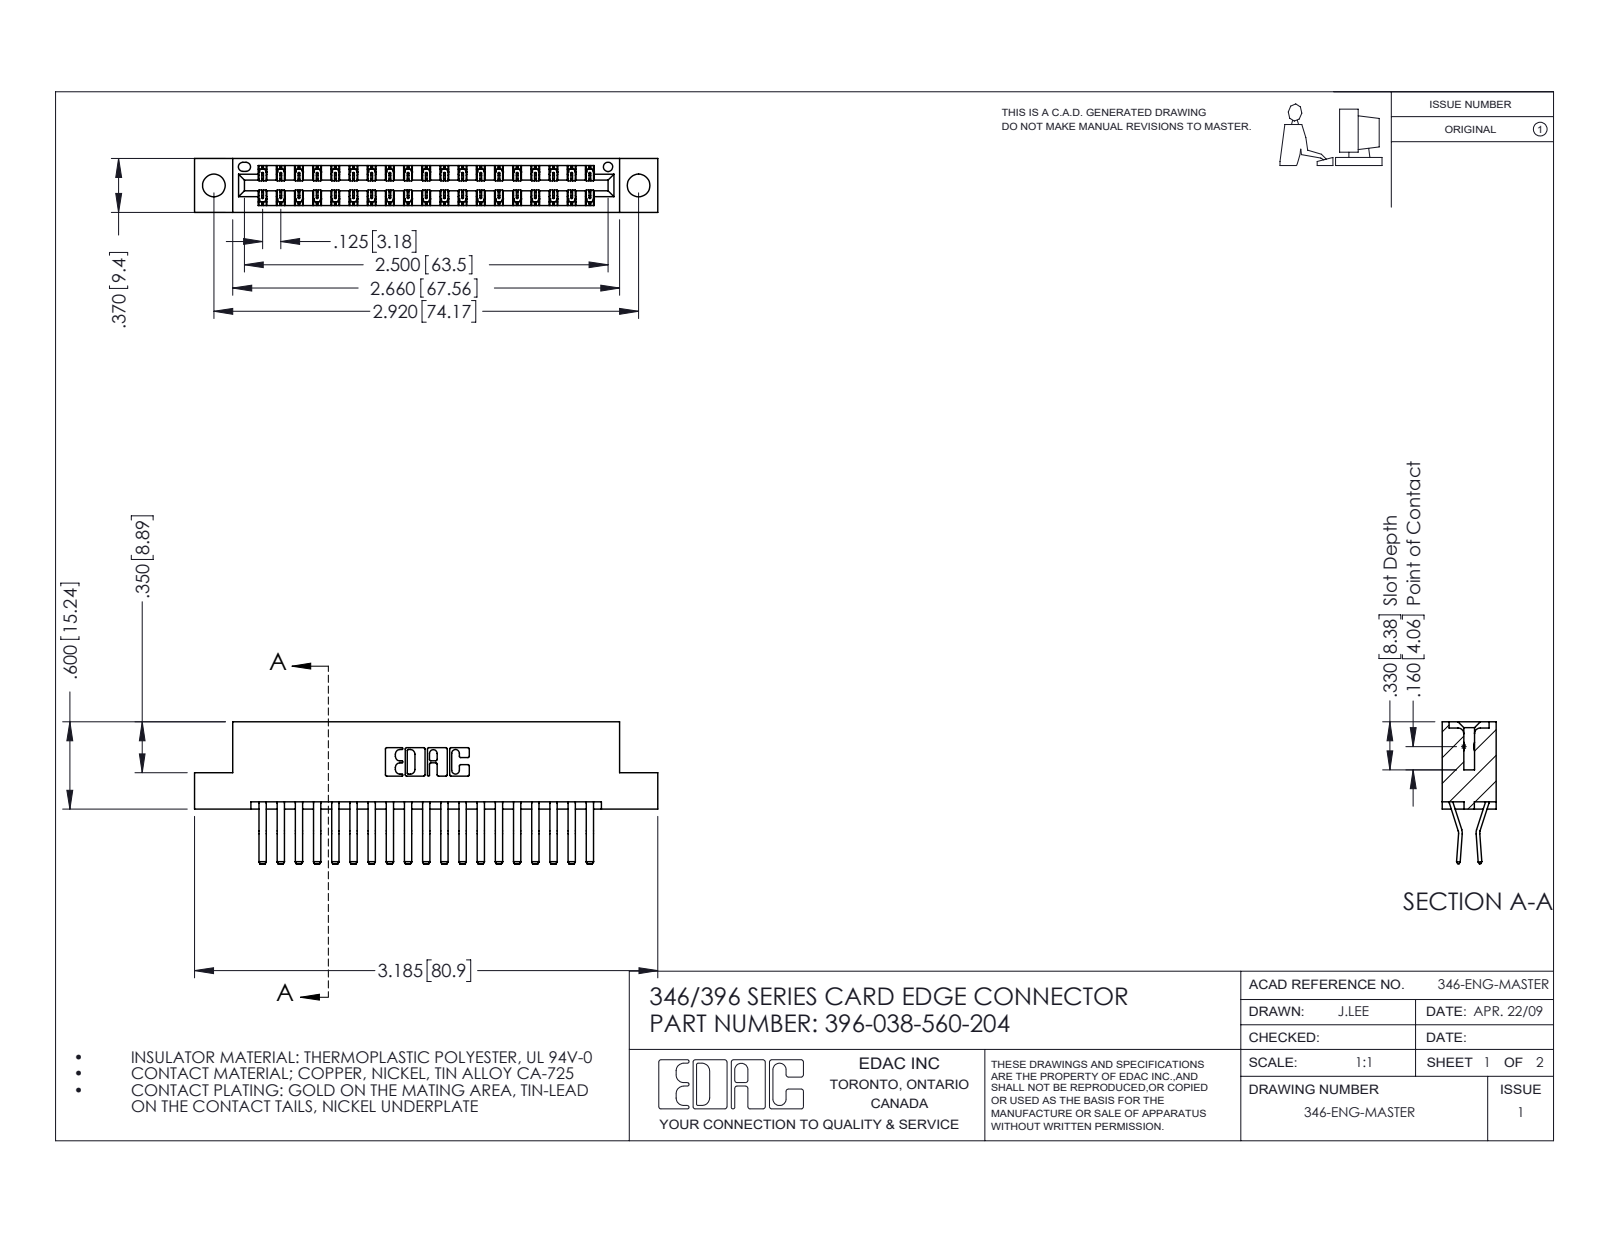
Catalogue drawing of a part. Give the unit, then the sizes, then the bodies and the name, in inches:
Units: inches
Overall size (bounding box): 3.185 × 0.975 × 0.37
Round holes (diameter × count): ⌀0.156 ×2, ⌀0.064 ×1
Partial cylindrical surfaces — rounded edges, fillets, slot ends (radius × count): R0.006 ×57, R0.01 ×22, R0.007 ×6, R0.031 ×6, R0.026 ×3, R0.01 ×2, R0.014 ×2, R0.022 ×2
Main face-to-face distances: 0.048, 0.322, 0.25, 0.37, 0.025, 0.072, 0.298, 0.275, 0.148, 0.222
Hole centre spacings: 0.246, 2.713, 2.92
Volume: 0.48 in³ · Surface area: 16.95 in²
Bodies: 39 solids, 2174 faces (1406 planar, 768 cylindrical, 0 other)
Part name (STEP PRODUCT): 396-038-560-204; 346 Part_Flush Mounting Lugs - 0.156 Dia-TH; 345-292-001_560 Tail
STEP written by: SolidWorks 2016 (CONFIG_CONTROL_DESIGN)
